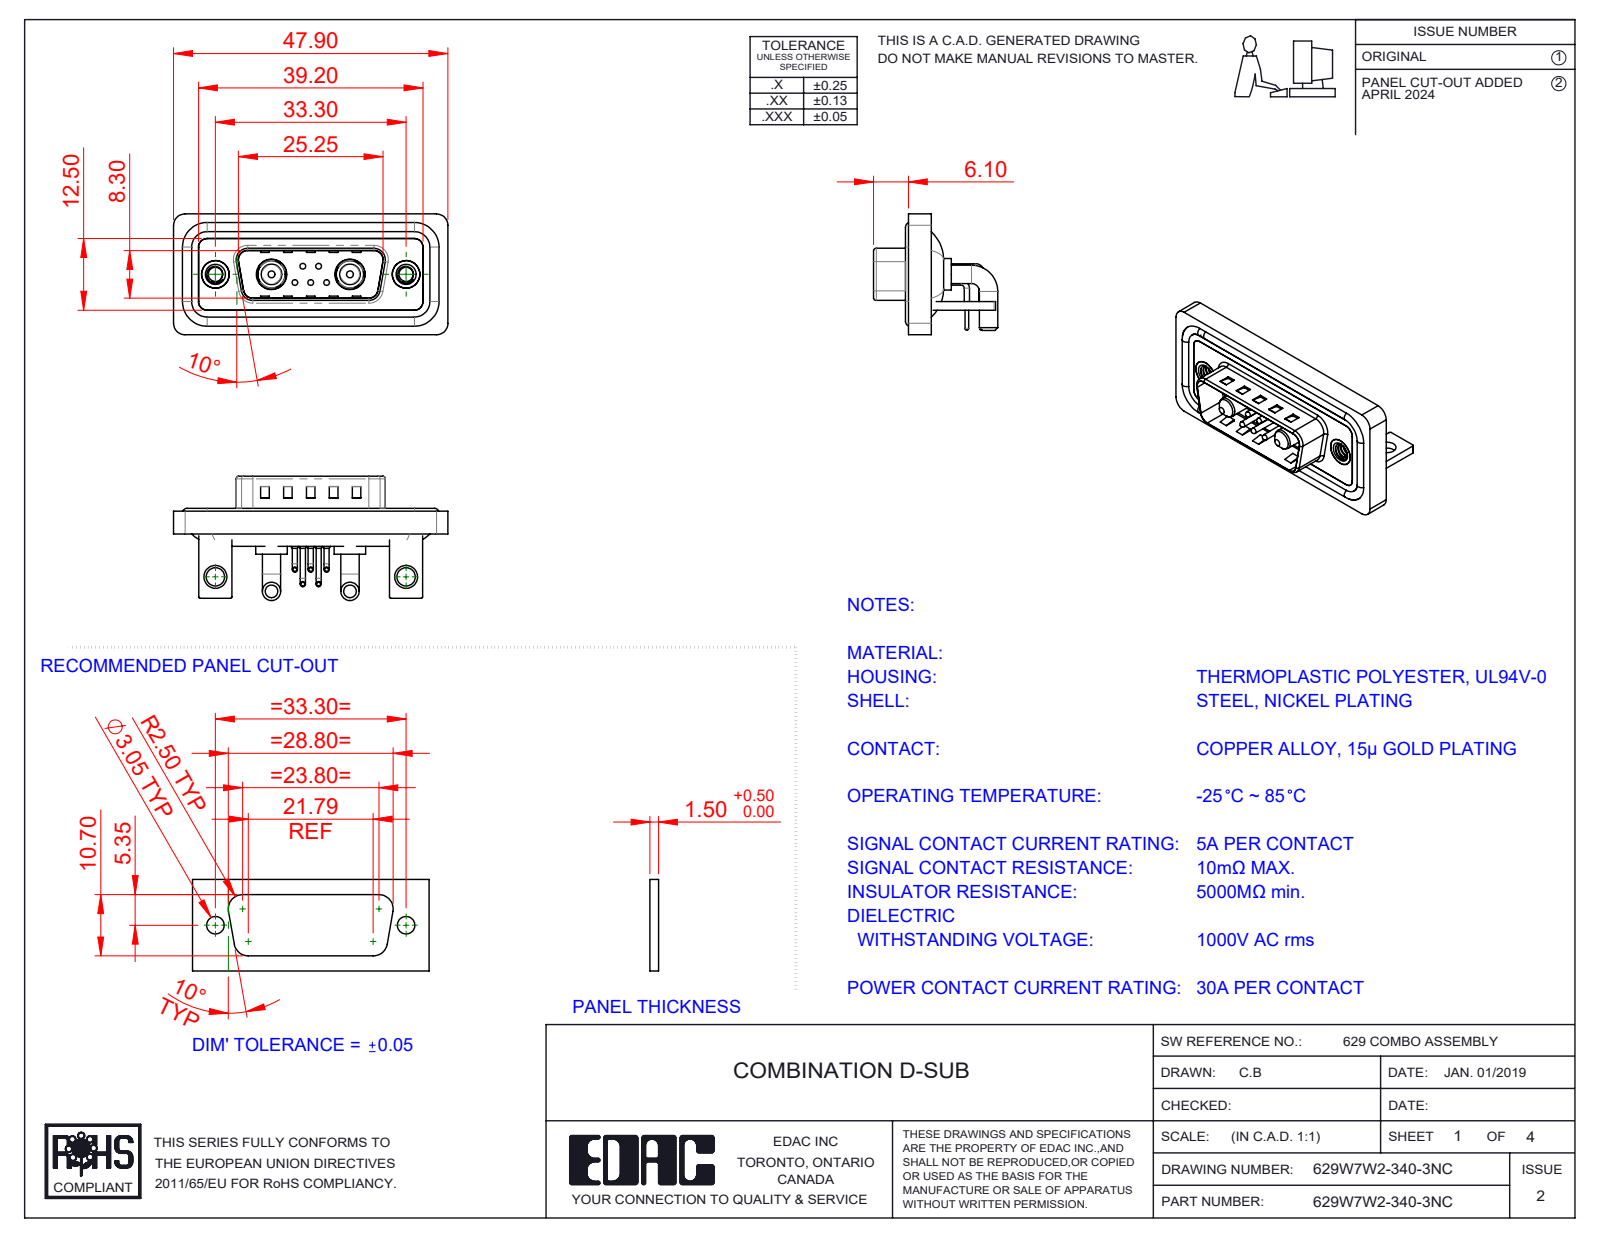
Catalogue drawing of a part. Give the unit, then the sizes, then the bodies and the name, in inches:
Units: inches
Overall size (bounding box): 1.886 × 0.854 × 0.831
Round holes (diameter × count): ⌀0.03 ×5, ⌀0.063 ×5, ⌀0.079 ×5, ⌀0.098 ×2, ⌀0.126 ×2, ⌀0.157 ×2, ⌀0.189 ×2, ⌀0.191 ×2, ⌀0.197 ×2, ⌀0.209 ×2
Round bosses / shafts (diameter × count): ⌀0.035 ×10, ⌀0.059 ×5, ⌀0.039 ×5, ⌀0.026 ×5, ⌀0.126 ×4, ⌀0.063 ×4, ⌀0.217 ×2, ⌀0.205 ×2
Partial cylindrical surfaces — rounded edges, fillets, slot ends (radius × count): R0.079 ×21, R0.059 ×18, R0.01 ×16, R0.02 ×9, R0.063 ×8, R0.04 ×5, R0.024 ×4, R0.026 ×4
Main face-to-face distances: 0.016, 0.059, 0.031, 0.114, 0.083, 0.043, 0.063, 0.047, 0.146, 0.177
Hole centre spacings: 0.124, 0.109, 0.386, 0.925, 1.311, 0.17, 0.17, 0.198
Volume: 0.367 in³ · Surface area: 15.14 in²
Bodies: 18 solids, 1121 faces (537 planar, 424 cylindrical, 160 other)
Part name (STEP PRODUCT): 629Combo Shell Front_15 Contacts; 629Combo Housing_7W2; 629Combo Contact Row 2; Power Pin_30A RA (+6 more)
STEP written by: SolidWorks 2023 (CONFIG_CONTROL_DESIGN)
